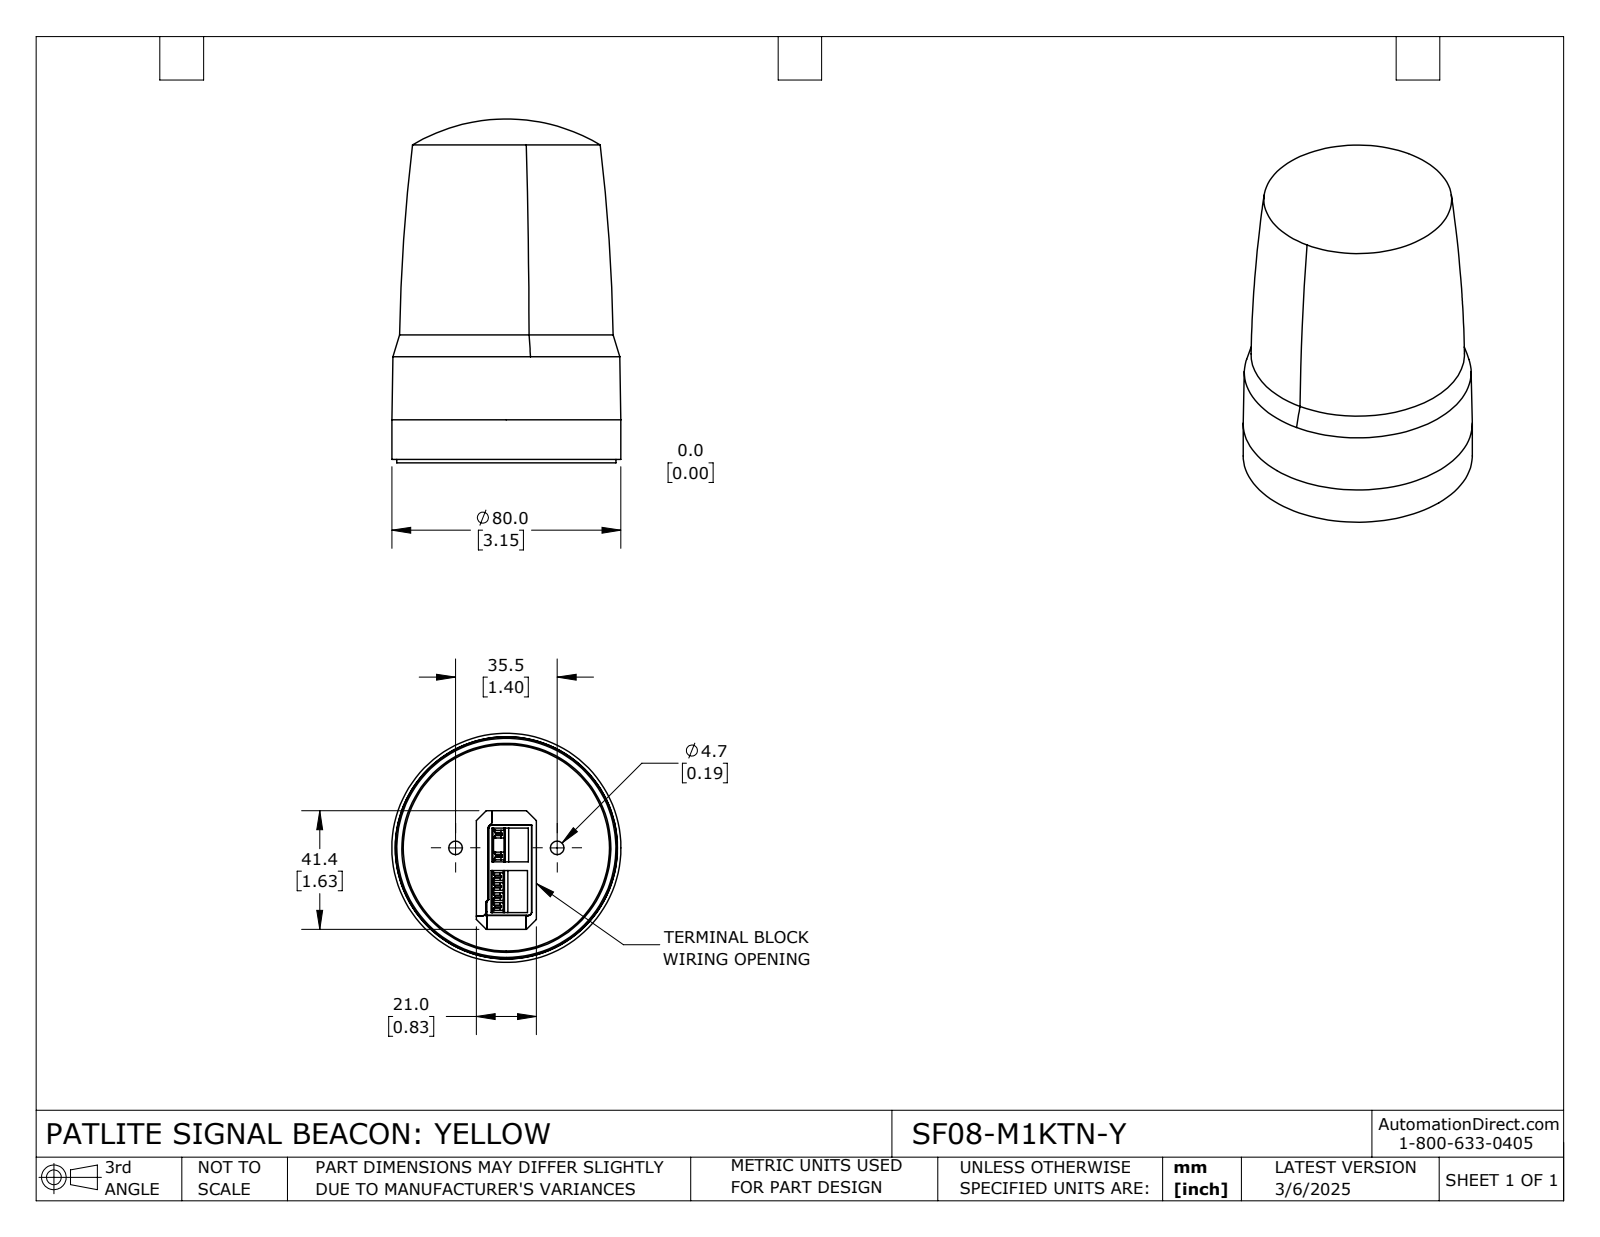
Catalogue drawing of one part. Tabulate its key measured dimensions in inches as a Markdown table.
| quantity | value |
| --- | --- |
| part name | SF08-M1KTN-Y |
| STEP written by | SolidWorks 2024 (CONFIG_CONTROL_DESIGN) |
| units | inches |
| bodies | 2 solids, 287 faces (199 planar, 23 cylindrical, 65 other) |
| overall size | 4.724 × 3.15 × 3.15 |
| volume | 29.01 in³ |
| surface area | 81.21 in² |
| round holes (diameter × count) | 0.185 × 2, 0.48 × 2, 2.874 × 1 |
| round bosses / shafts (diameter × count) | 3.15 × 1, 3.012 × 1, 2.937 × 1, 2.835 × 1 |
| partial cylindrical surfaces (radius × count) | 1.319 × 1, 1.362 × 1 |
| main face-to-face distances | 0.248, 0.185, 0.433, 0.071, 0.504, 0.256, 0.059, 0.374, 0.126, 0.13 |
| hole center spacings | 0.699, 1.398 |
